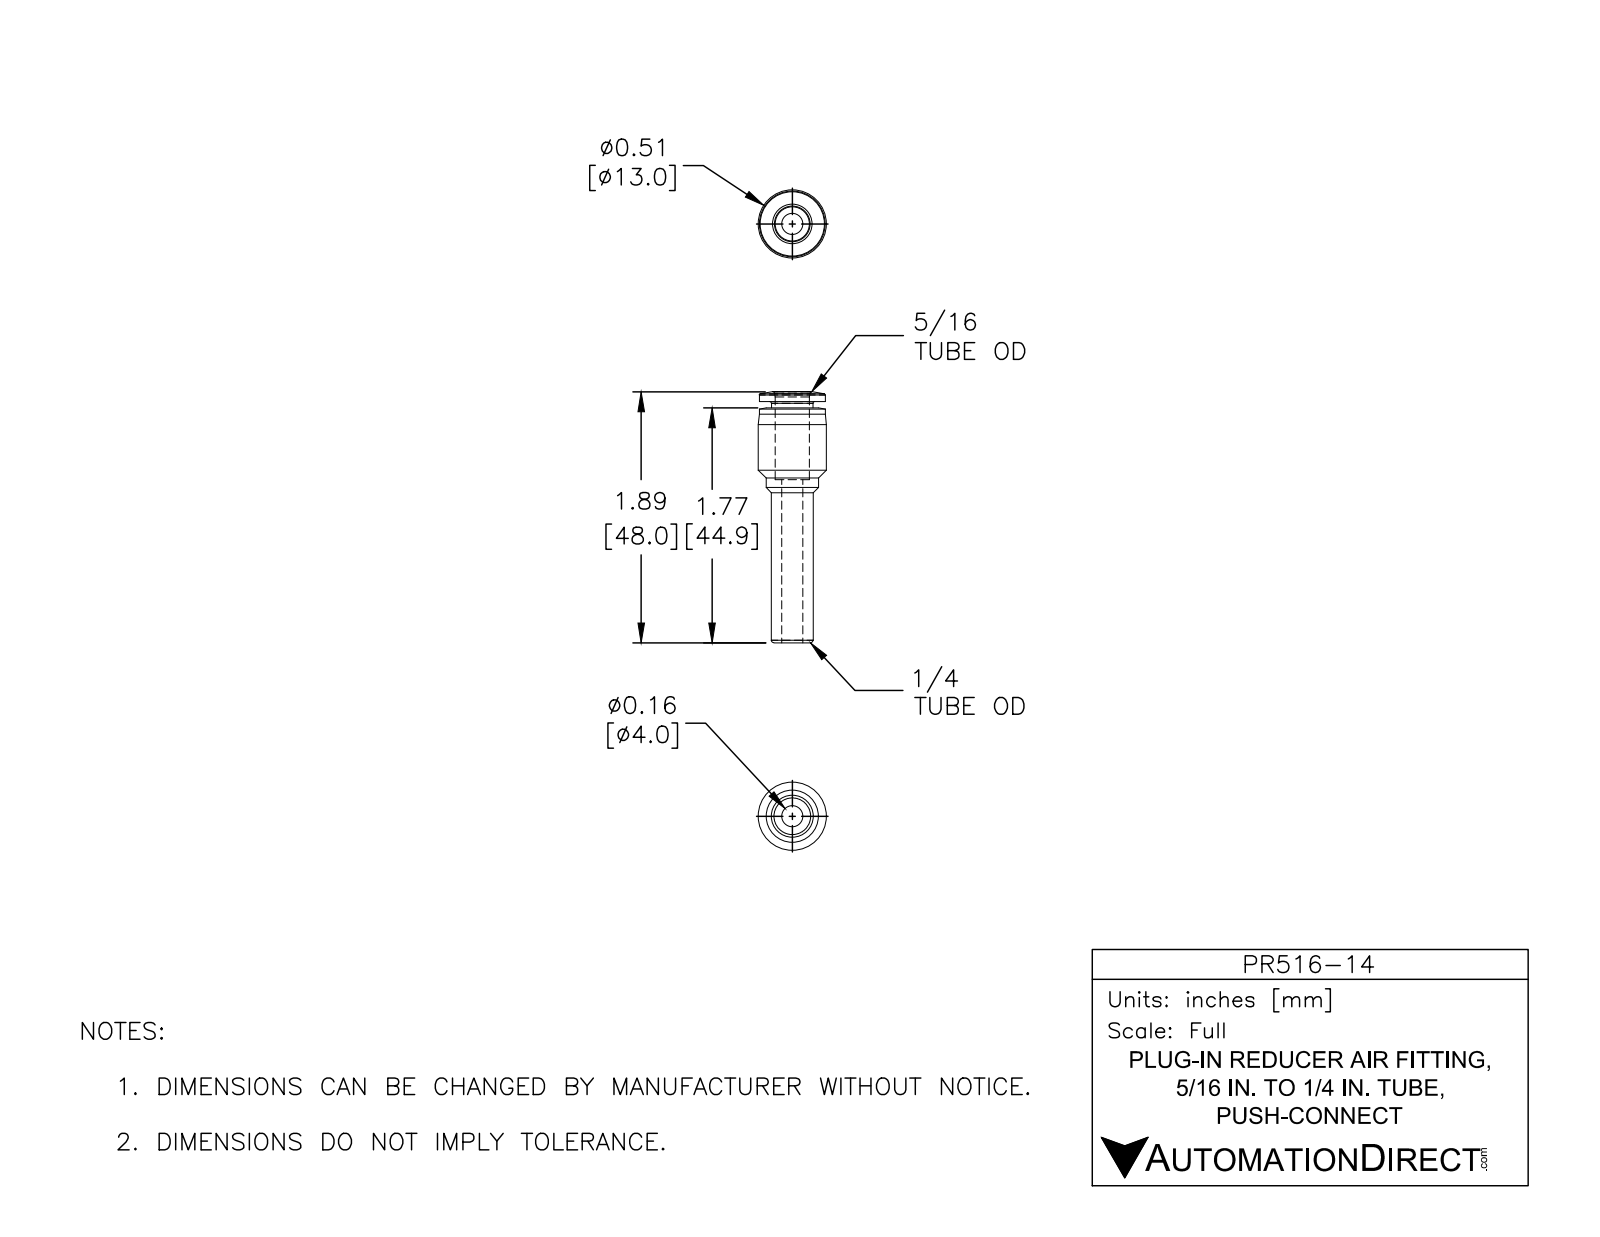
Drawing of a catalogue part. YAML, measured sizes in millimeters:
part_name: "PR516-14"
step_written_by: "SolidWorks 2015 (CONFIG_CONTROL_DESIGN)"
units: millimeters
bodies: {solids: 1, faces: 40, planar: 4, cylindrical: 16, other: 20}
overall_size: [48, 13, 13]
volume: 2670
surface_area: 2481
round_holes:
  - {diameter: 4, count: 1}
  - {diameter: 6.6, count: 1}
round_bosses_or_shafts:
  - {diameter: 13, count: 1}
  - {diameter: 12.6, count: 1}
  - {diameter: 10, count: 1}
  - {diameter: 8, count: 1}
  - {diameter: 8, count: 1}
face_to_face_distances: [1.2, 44.9, 46.1, 31.2, 13.7, 14.9]
